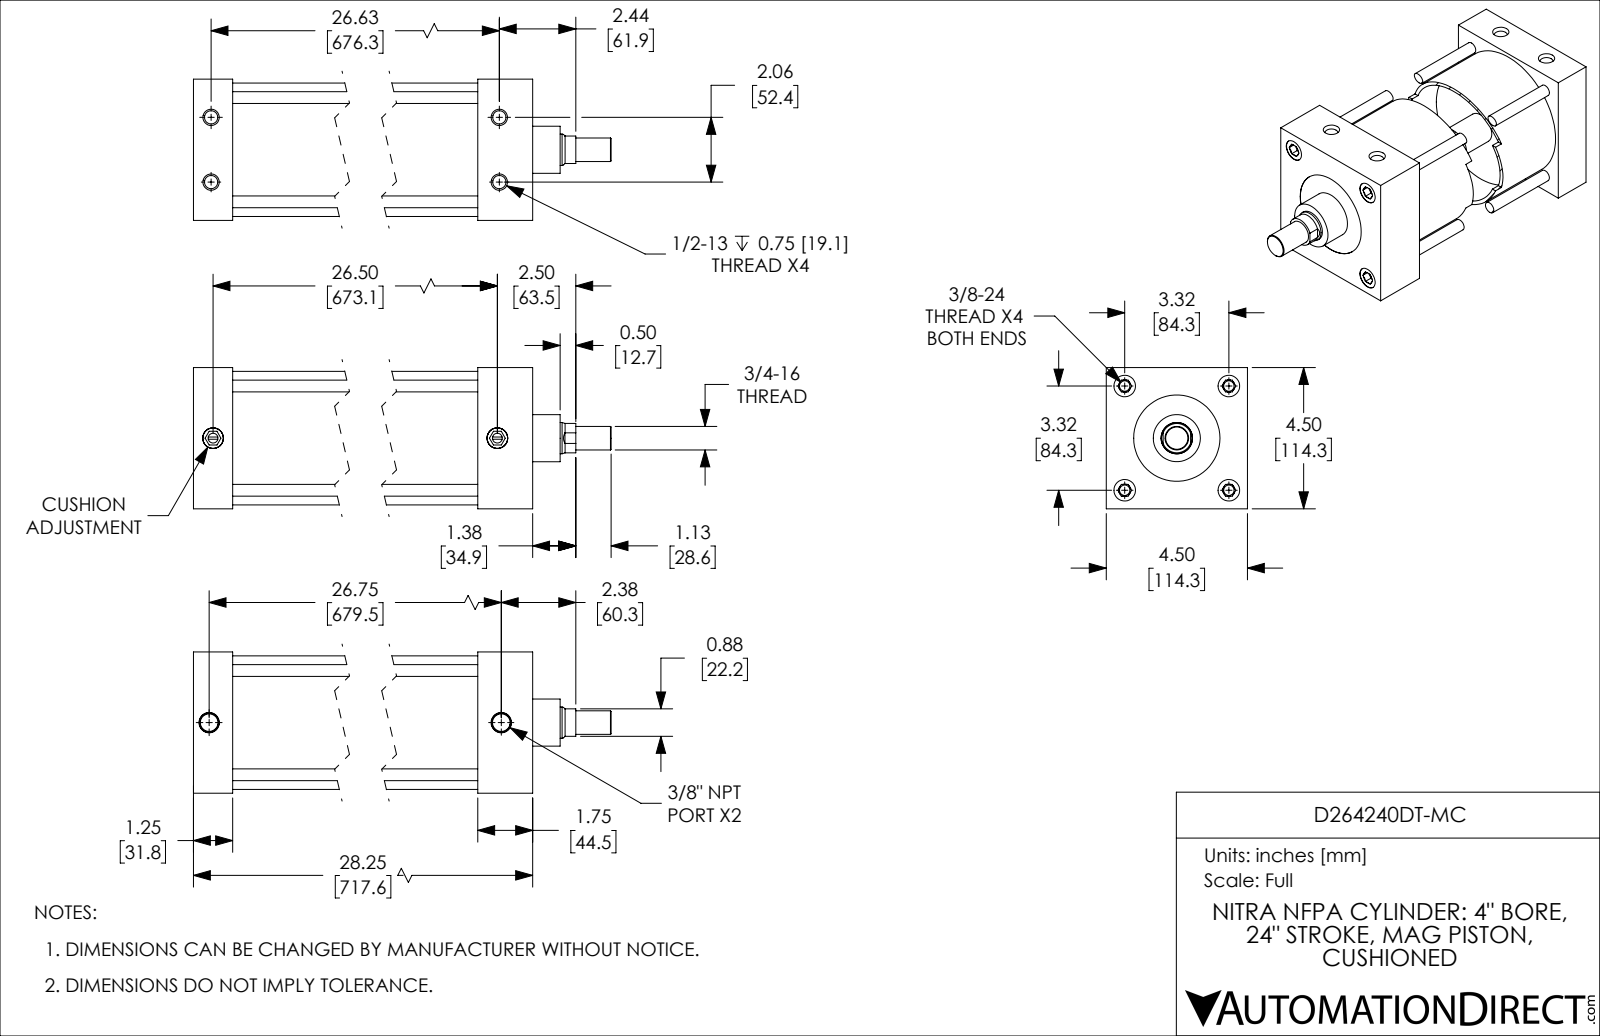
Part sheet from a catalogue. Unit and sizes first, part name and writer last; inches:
Units: inches
Overall size (bounding box): 30.75 × 4.5 × 4.5
Round holes (diameter × count): ⌀0.332 ×4, ⌀0.422 ×4, ⌀0.687 ×4, ⌀0.312 ×2, ⌀0.562 ×2, ⌀0.656 ×2, ⌀1.001 ×1, ⌀2.75 ×1, ⌀4.001 ×1
Round bosses / shafts (diameter × count): ⌀0.375 ×4, ⌀0.657 ×2, ⌀4.251 ×1, ⌀3.999 ×1, ⌀1.5 ×1, ⌀0.999 ×1, ⌀0.75 ×1
Partial cylindrical surfaces — rounded edges, fillets, slot ends (radius × count): R0.469 ×1
Main face-to-face distances: 1.25, 4.5, 26.5, 25.25, 28.25, 27, 1.75, 2.5, 24, 25.75
Hole centre spacings: 1.033, 2.347, 3.32, 26.707, 2.062, 4.695, 26.625, 26.705
Volume: 147.3 in³ · Surface area: 1 067 in²
Bodies: 4 solids, 246 faces (90 planar, 78 cylindrical, 78 other)
Part name (STEP PRODUCT): D264240DT-MC_BODY; D264240DT-MC_CUSHION; D264240DT-MC; D264240DT-MC_PISTON_KK1
STEP written by: SolidWorks 2019 (CONFIG_CONTROL_DESIGN)
